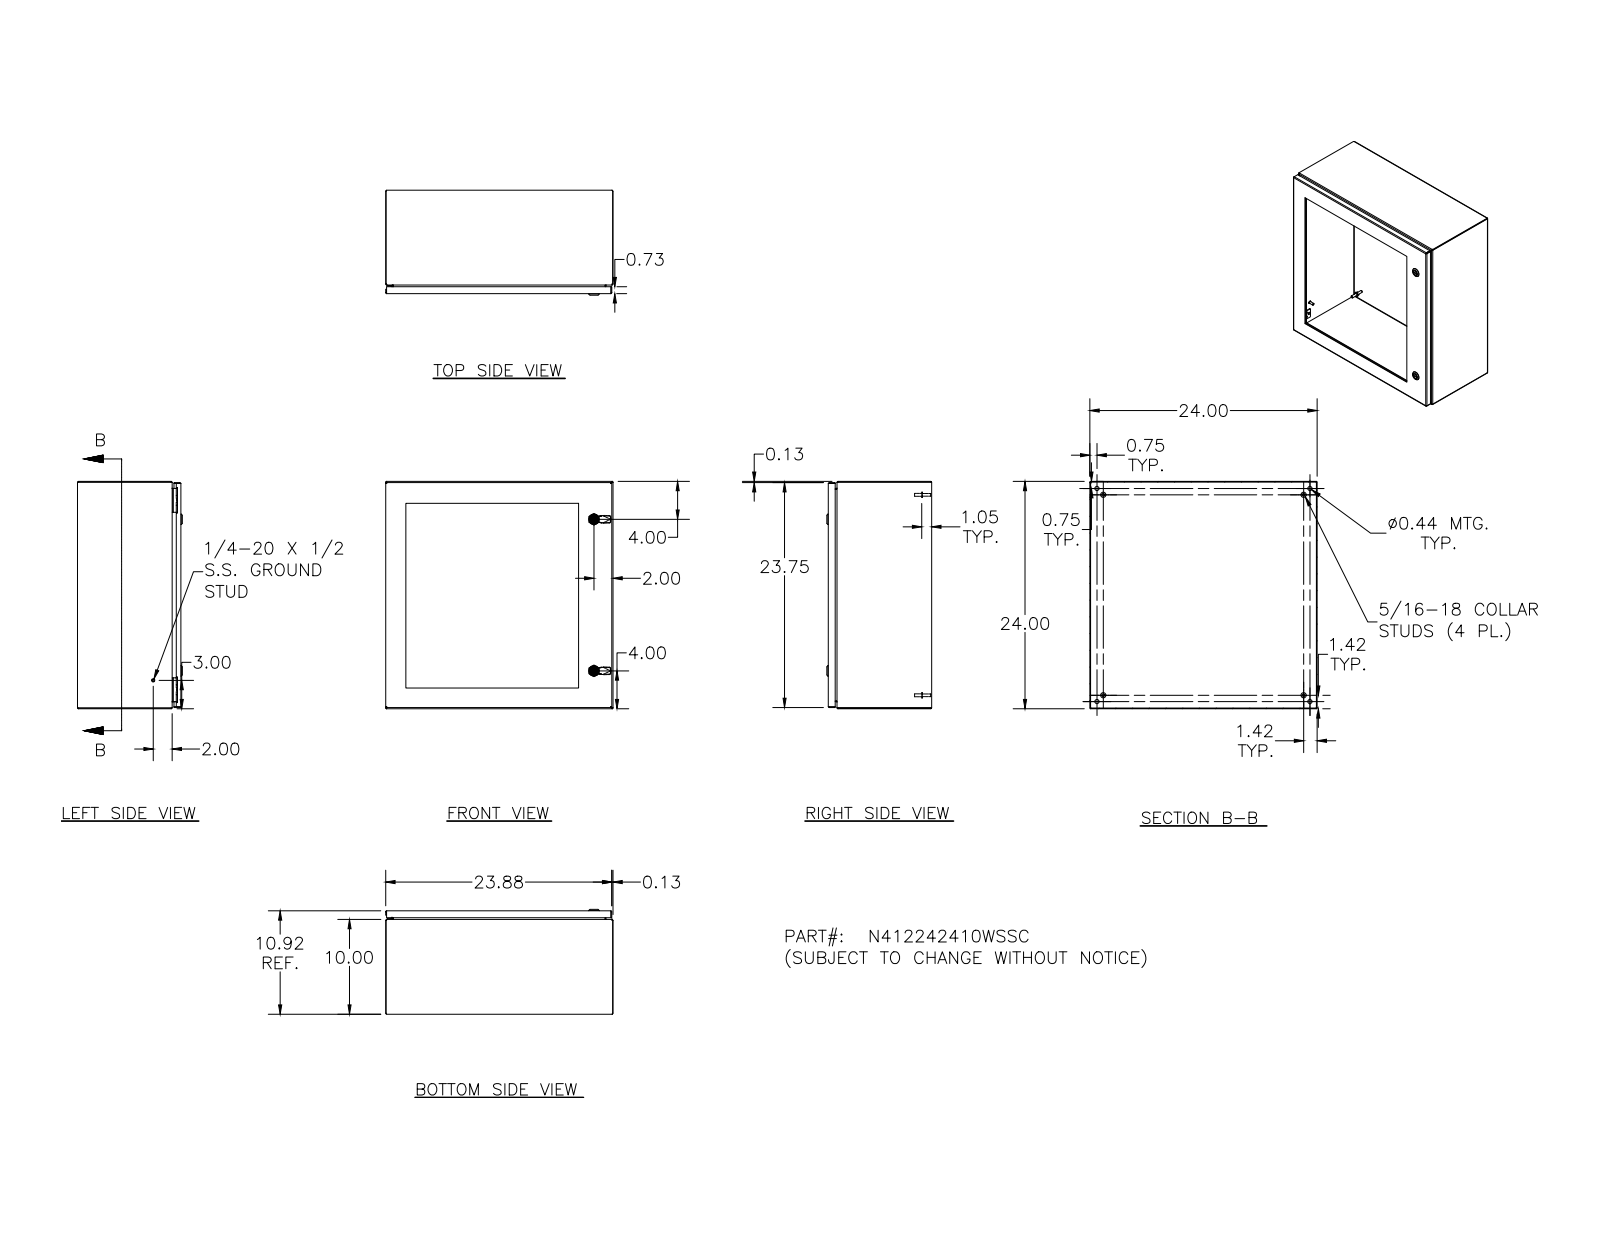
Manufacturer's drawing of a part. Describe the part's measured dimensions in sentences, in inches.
The part is named "N412242410WSSC; N412242410WSSCBKP; N4122424WSSCLID; HFW328176 (+8 more)". Its 3-D file was written by "Autodesk Inventor 2011 (AUTOMOTIVE_DESIGN)". It is 86 solids with 2366 faces: 973 planar, 672 cylindrical and 721 other. Overall it measures 24 by 24 by 11.075 inches. Its volume is 250.2 cubic inches and its surface area 4 942 square inches. Round holes: 22 of diameter 0.156, 20 of diameter 0.281, 4 of diameter 0.093, 4 of diameter 0.152, 4 of diameter 0.167, 4 of diameter 0.172, 4 of diameter 0.188, 4 of diameter 0.437, 2 of diameter 0.197, 2 of diameter 0.315, 2 of diameter 0.394, 2 of diameter 0.402. Round bosses or shafts: 20 of diameter 0.19, 19 of diameter 0.253, 10 of diameter 0.25, 4 of diameter 0.563, 4 of diameter 0.36, 4 of diameter 0.32, 4 of diameter 0.3, 4 of diameter 0.275. Partial cylindrical surfaces (rounded edges, fillets, slot ends): 34 of radius 0.031, 26 of radius 0.05, 24 of radius 0.105, 18 of radius 0.016, 16 of radius 0.125, 15 of radius 0.02, 8 of radius 0.032, 8 of radius 0.157. The main face-to-face distances are 0.074, 23.926, 10.843, 10.769, 23.852, 24, 0.25, 10.593, 10.519, 10.917. The hole center spacings are 4, 8, 21.132, 12, 19.906, 20, 22.239, 20.75.
